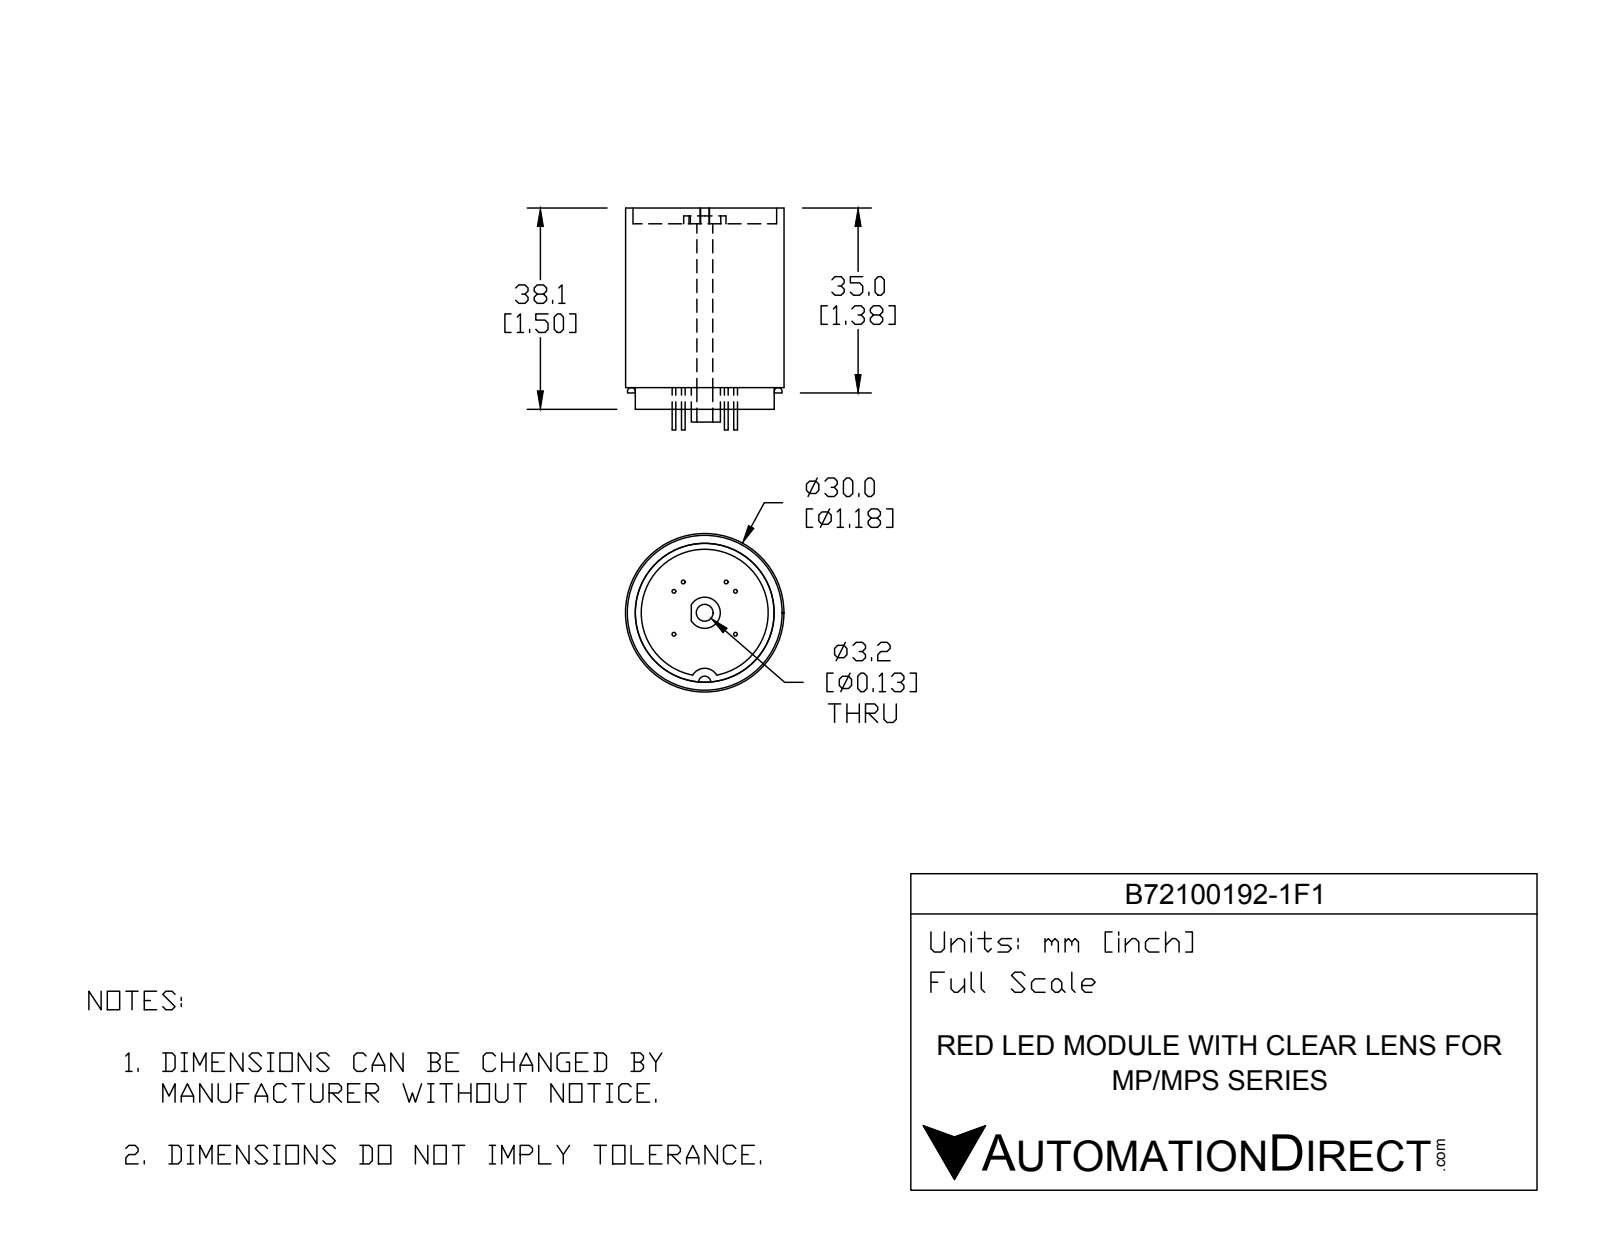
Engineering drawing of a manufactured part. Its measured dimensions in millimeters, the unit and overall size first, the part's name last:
Units: millimetres
Overall size (bounding box): 42 × 30 × 30
Round holes (diameter × count): ⌀3 ×1, ⌀6.06 ×1, ⌀24.04 ×1, ⌀27.2 ×1
Round bosses / shafts (diameter × count): ⌀0.7 ×6, ⌀30 ×1, ⌀26.3 ×1, ⌀8 ×1, ⌀5.9 ×1
Partial cylindrical surfaces — rounded edges, fillets, slot ends (radius × count): R0.9 ×1, R1.15 ×1, R2.65 ×1
Main face-to-face distances: 31, 34, 3, 4.1, 35.1, 38.1, 1.5, 36.6, 32.5, 2.42
Volume: 22 787 mm³ · Surface area: 6 668 mm²
Bodies: 10 solids, 64 faces (25 planar, 35 cylindrical, 4 other)
Part name (STEP PRODUCT): B72100192-1F1
STEP written by: SolidWorks 2016 (AUTOMOTIVE_DESIGN)
